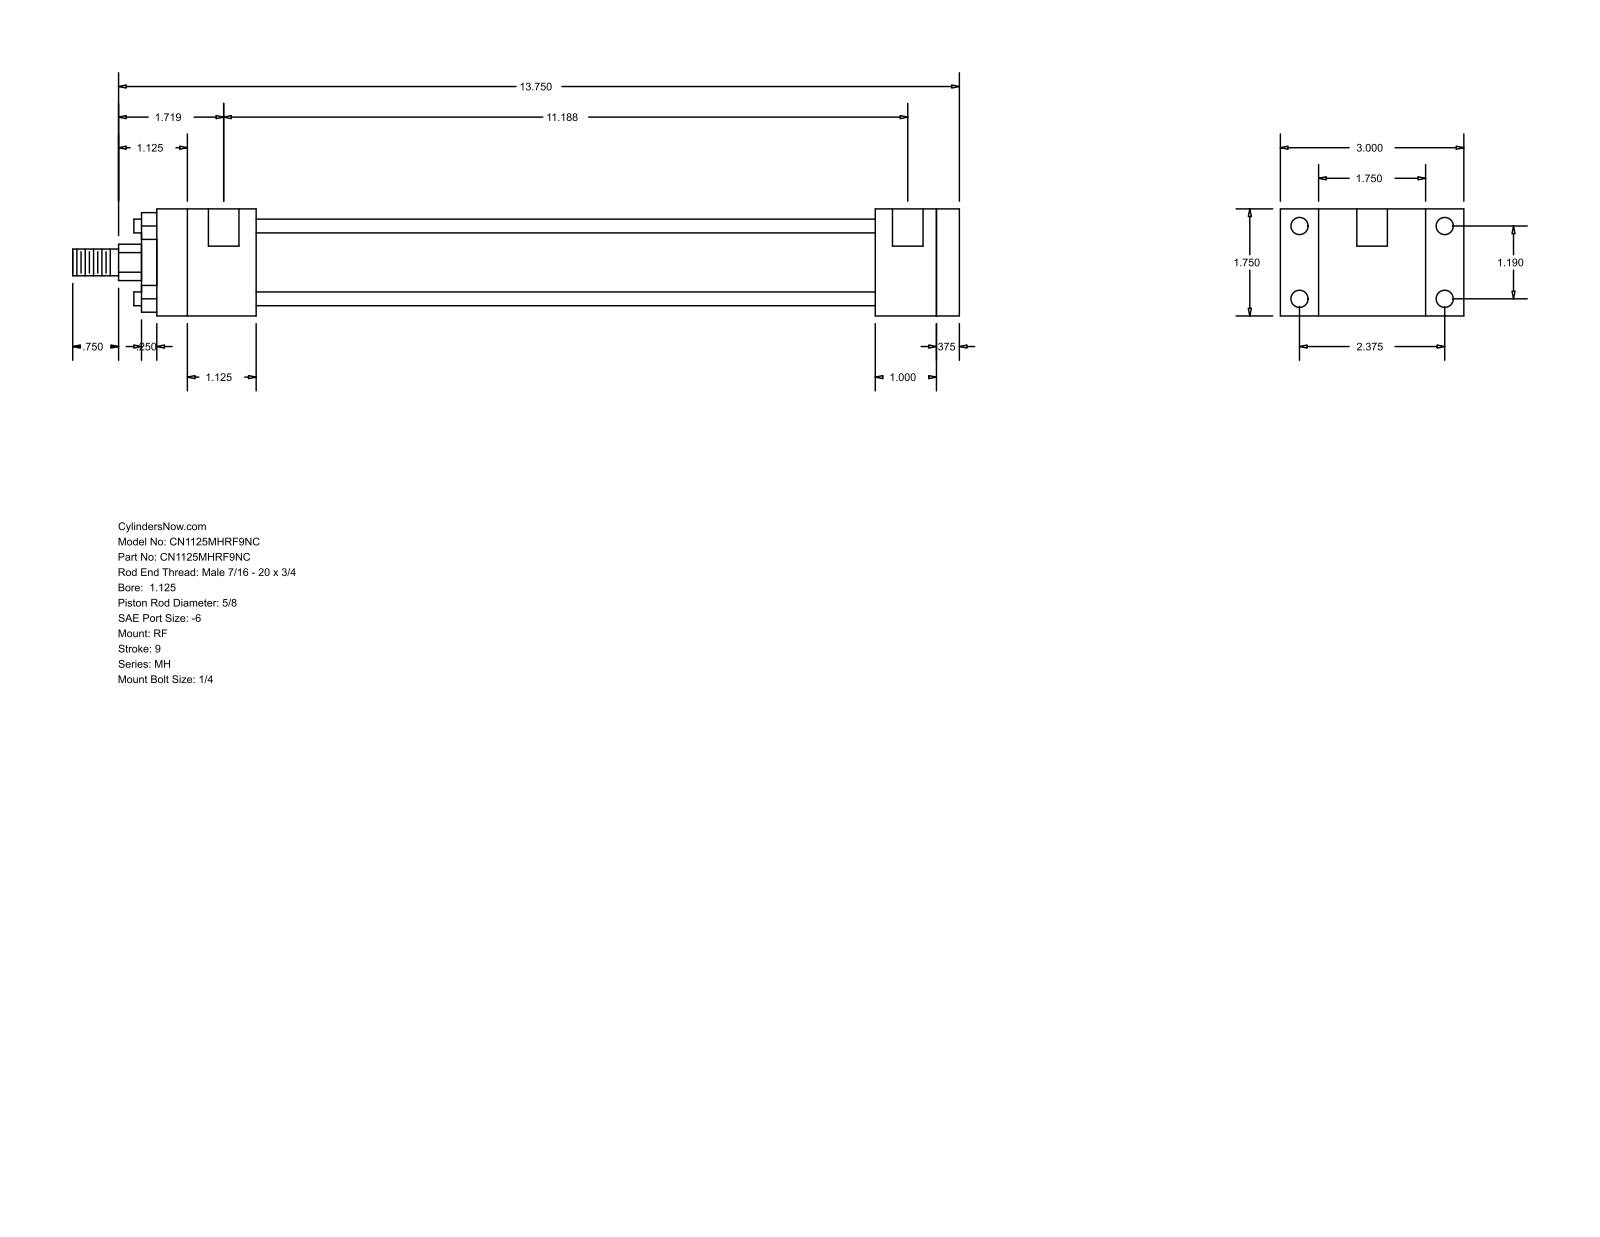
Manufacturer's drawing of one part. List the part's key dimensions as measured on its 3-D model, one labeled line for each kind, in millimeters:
Part name (STEP PRODUCT): MH_RF__0112_0.625
STEP written by: GSSL Pune (CONFIG_CONTROL_DESIGN)
Units: millimetres
Bodies: 0 solids, 92 faces (64 planar, 28 cylindrical, 0 other)
Overall size (bounding box): 368.3 × 76.2 × 44.45
Round holes (diameter × count): ⌀5.56 ×4, ⌀7.14 ×4, ⌀12.7 ×2
Round bosses / shafts (diameter × count): ⌀5.71 ×4, ⌀34.92 ×1, ⌀28.57 ×1, ⌀15.88 ×1, ⌀11.11 ×1
Partial cylindrical surfaces — rounded edges, fillets, slot ends (radius × count): R7.54 ×1
Main face-to-face distances: 44.46, 9.52, 34.93, 333.37, 15.87, 282.58, 292.1, 257.17, 25.41, 41.27
Hole centre spacings: 30.22, 60.32, 67.47, 280.99, 3.17, 284.16
